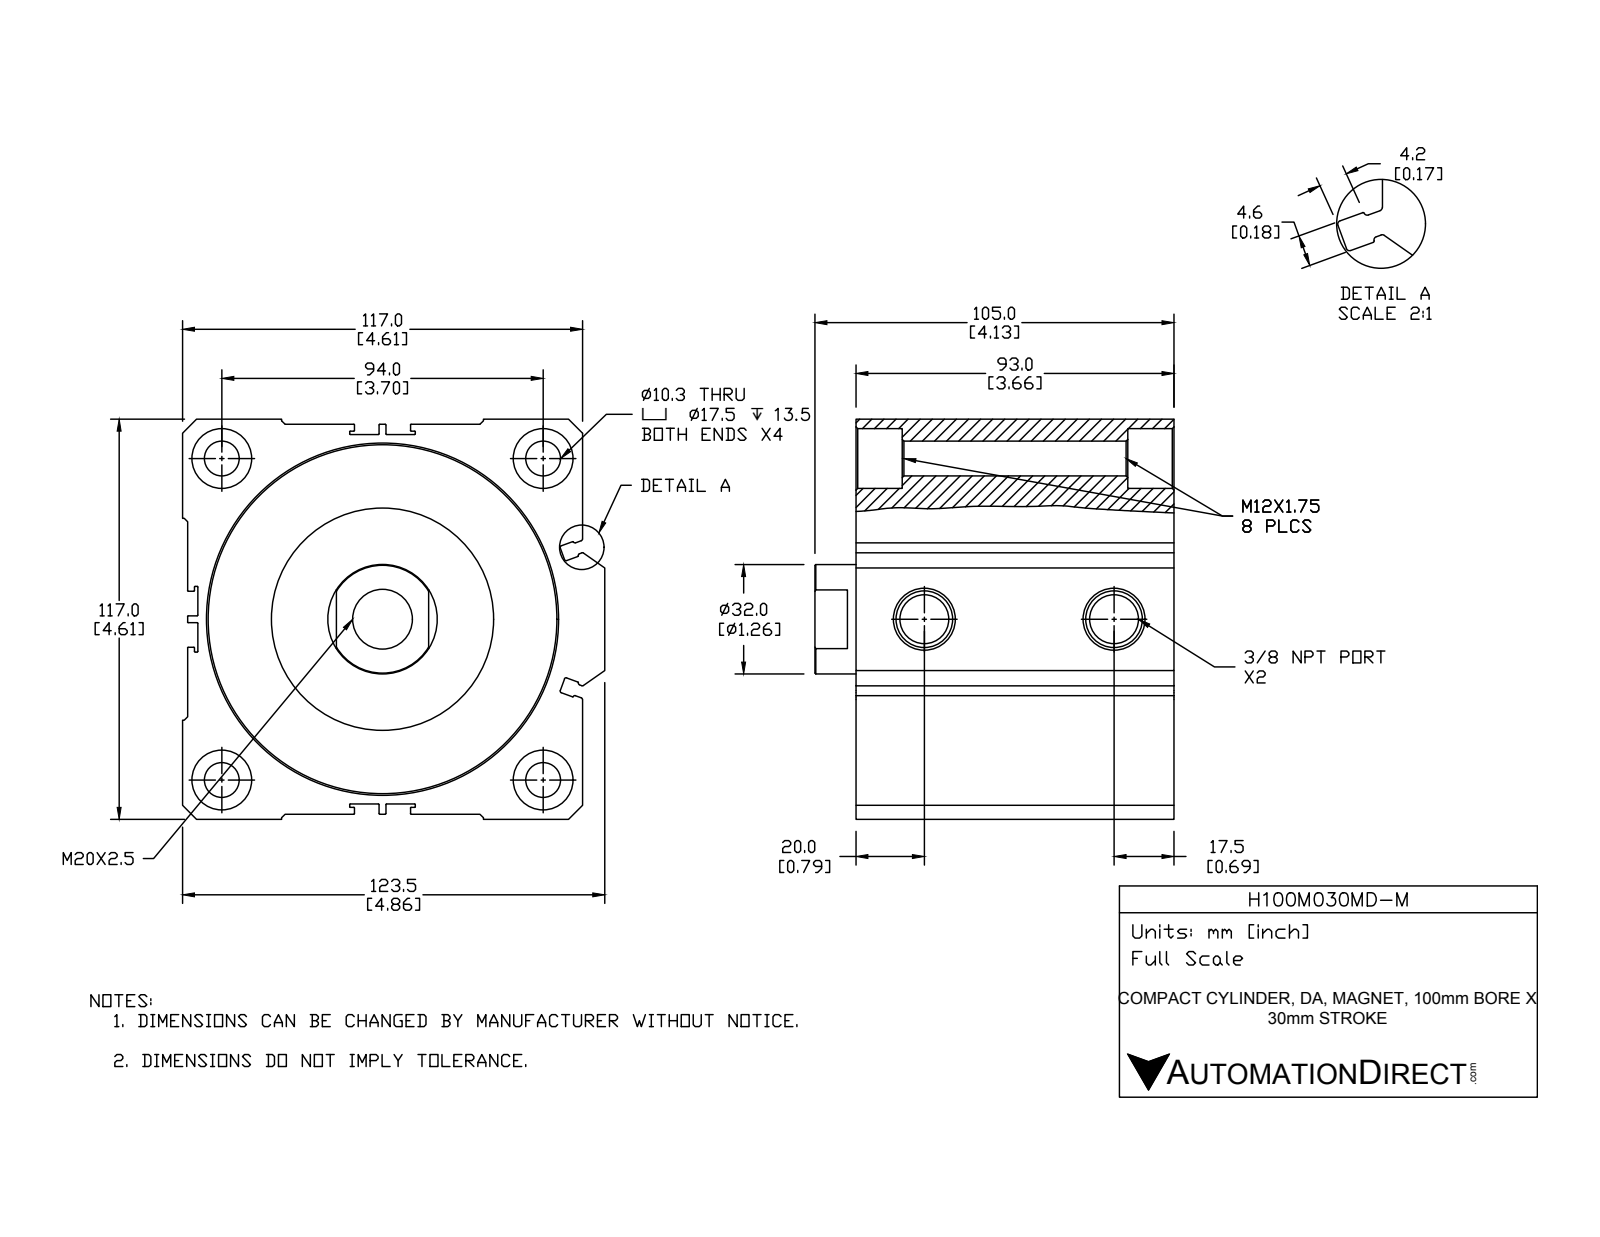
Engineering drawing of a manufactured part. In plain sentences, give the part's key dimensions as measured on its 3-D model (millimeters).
The part is named "H100M030MD-M; H100M030MD-M-BODY; H100M030MD-M-PISTON". Its 3-D file was written by "SolidWorks 2015 (CONFIG_CONTROL_DESIGN)". It is 2 solids with 261 faces: 105 planar, 103 cylindrical and 53 other. Overall it measures 123.5 by 117 by 105 millimeters. Its volume is 917 750 cubic millimeters and its surface area 165 043 square millimeters. Round holes: 5 of diameter 17.5, 4 of diameter 10.2, 2 of diameter 14.27, 1 of diameter 32, 1 of diameter 65, 1 of diameter 100, 1 of diameter 102. Round bosses or shafts: 1 of diameter 39. Partial cylindrical surfaces (rounded edges, fillets, slot ends): 40 of radius 0.2, 12 of radius 0.5. The main face-to-face distances are 1.5, 115.5, 117, 27.8, 58.5, 30.7, 12.5, 40.3, 71, 12. The hole center spacings are 66.47, 94, 132.94, 55.5.
